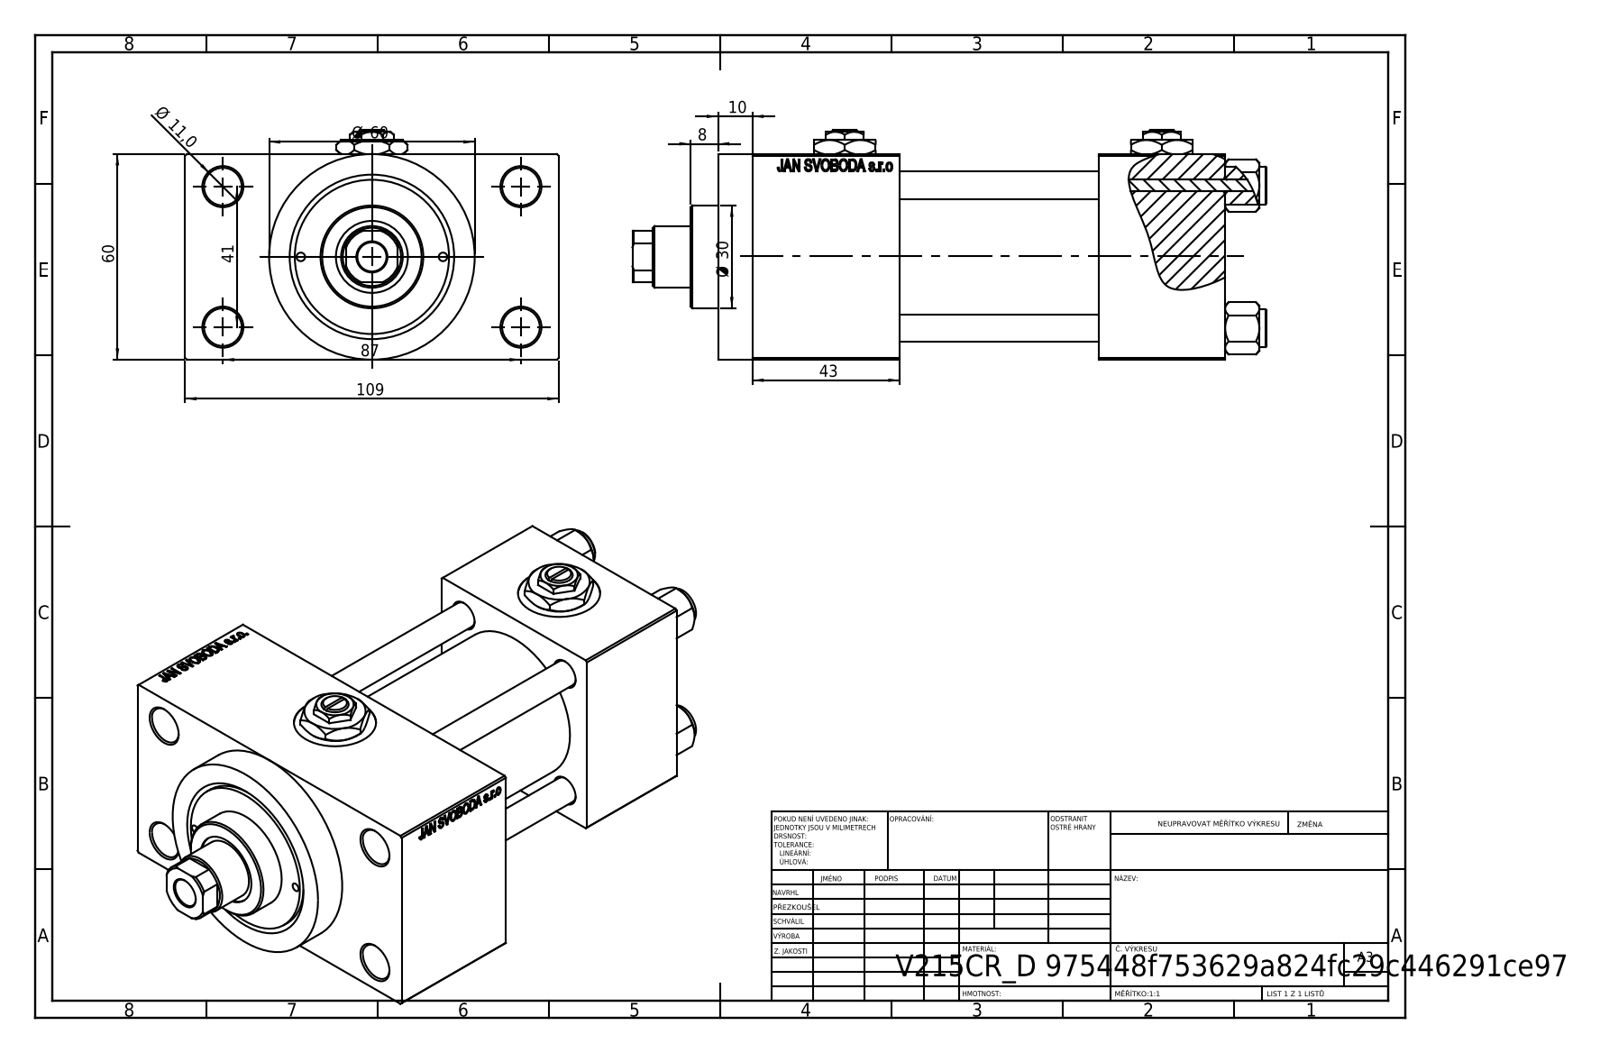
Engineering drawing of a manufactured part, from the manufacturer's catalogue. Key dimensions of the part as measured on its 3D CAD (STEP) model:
Part name (STEP PRODUCT): V215CR_D_TYCINKA; V215CR_VCP_D; V215_VC_A; V215CR_D_Body (+2 more)
STEP written by: SolidWorks 2019 (CONFIG_CONTROL_DESIGN)
Units: millimetres
Bodies: 13 solids, 1213 faces (548 planar, 103 cylindrical, 562 other)
Overall size (bounding box): 185 × 109 × 67
Volume: 510 125 mm³ · Surface area: 125 149 mm²
Round holes (diameter × count): ⌀8 ×4, ⌀11 ×4, ⌀16.66 ×4, ⌀24 ×4, ⌀7 ×3, ⌀2.5 ×2, ⌀8.5 ×1, ⌀18 ×1, ⌀21 ×1, ⌀31 ×1, ⌀40 ×1, ⌀45 ×1
Round bosses / shafts (diameter × count): ⌀11 ×4, ⌀60 ×1, ⌀46 ×1, ⌀30 ×1
Partial cylindrical surfaces — rounded edges, fillets, slot ends (radius × count): R8.5 ×1
Main face-to-face distances: 60, 58, 24.5, 84.5, 37, 95, 43, 138, 101, 10
Hole centre spacings: 20.85, 22.65, 29.49, 30.62, 41.7, 46.53, 47.15, 48.09
